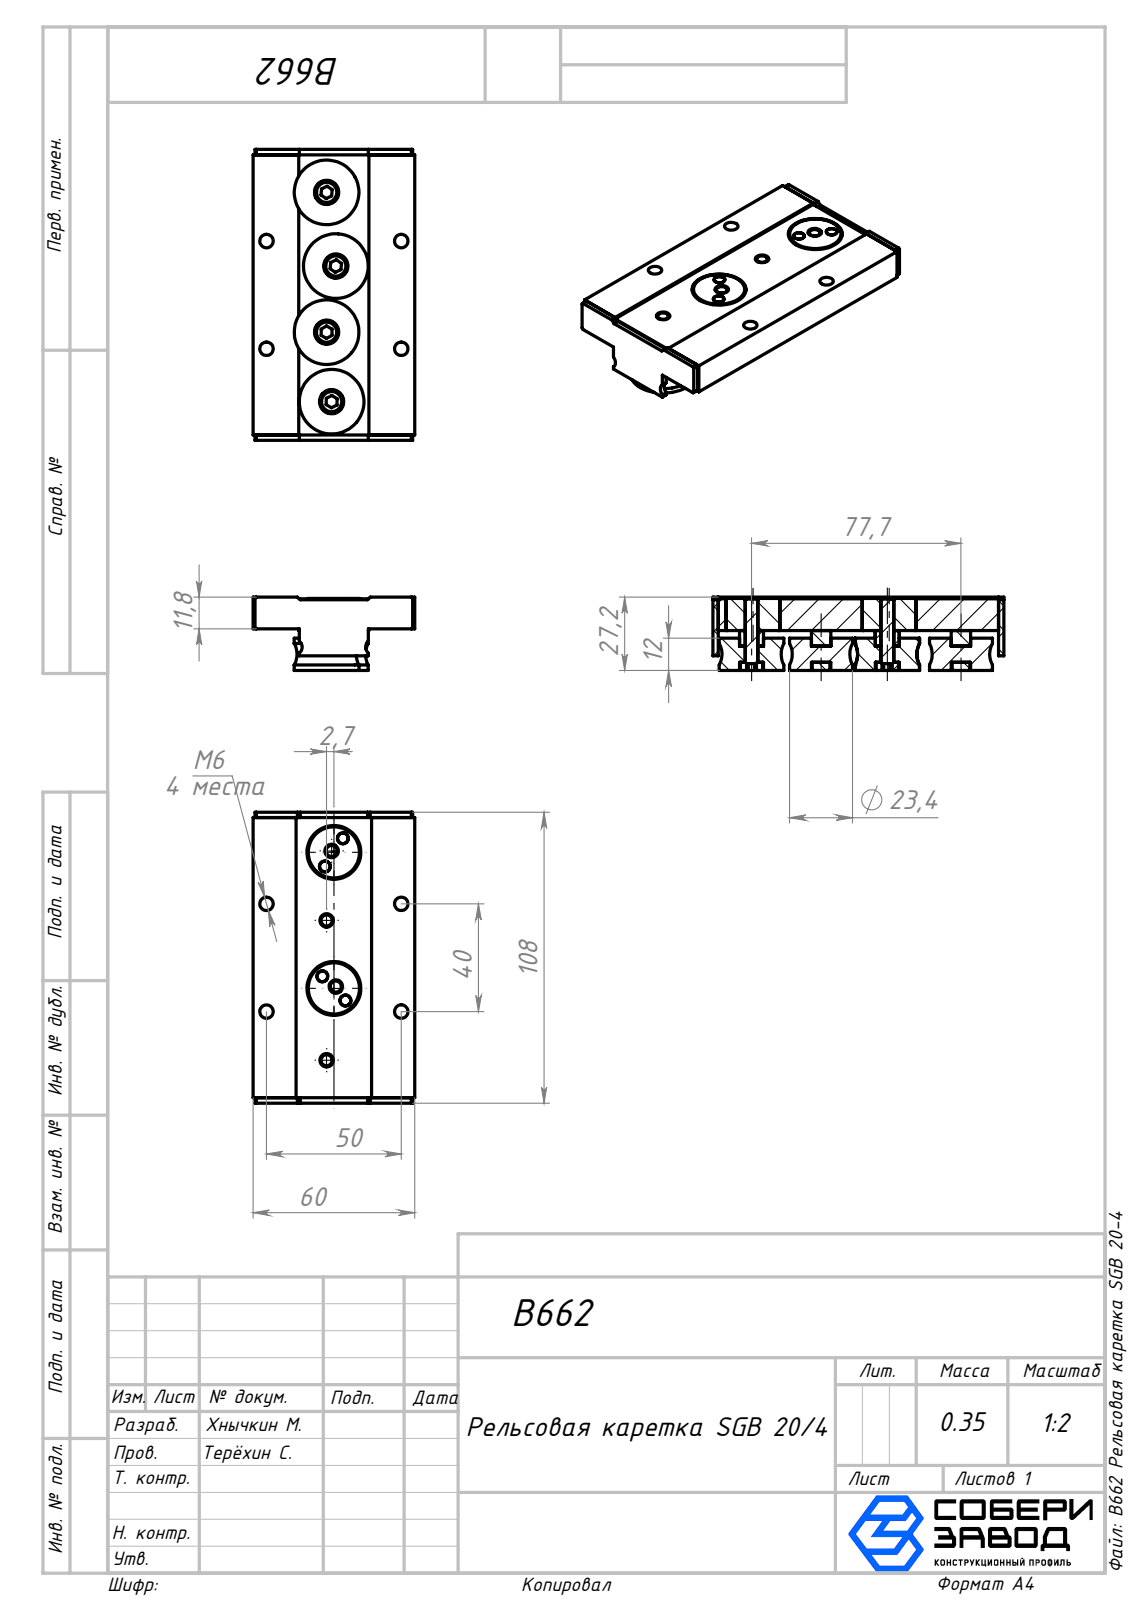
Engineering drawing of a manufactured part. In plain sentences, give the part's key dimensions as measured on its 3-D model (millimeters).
The part is named "B662 Ролик_00; B662 Рельсовая каретка SGB 20-4; B662 Заслонка_00; Каретка_00 (+3 more)". Its 3-D file was written by "SolidWorks 2025 (AUTOMOTIVE_DESIGN)". It is 21 solids with 296 faces: 122 planar, 126 cylindrical and 48 other. Overall it measures 108 by 60 by 27.2 millimeters. Its volume is 96 894 cubic millimeters and its surface area 38 005 square millimeters. Round holes: 8 of diameter 5, 4 of diameter 4, 4 of diameter 9, 2 of diameter 20. Round bosses or shafts: 4 of diameter 24, 4 of diameter 8.5. Partial cylindrical surfaces (rounded edges, fillets, slot ends): 4 of radius 0.5, 2 of radius 3.03. The main face-to-face distances are 11.8, 0.6, 12.4, 11.2, 2, 106, 27.2, 26.6, 15.4, 14.8. The hole center spacings are 6.2, 6.28, 12.4, 25.39, 26.44, 31.46, 40, 40.14.
